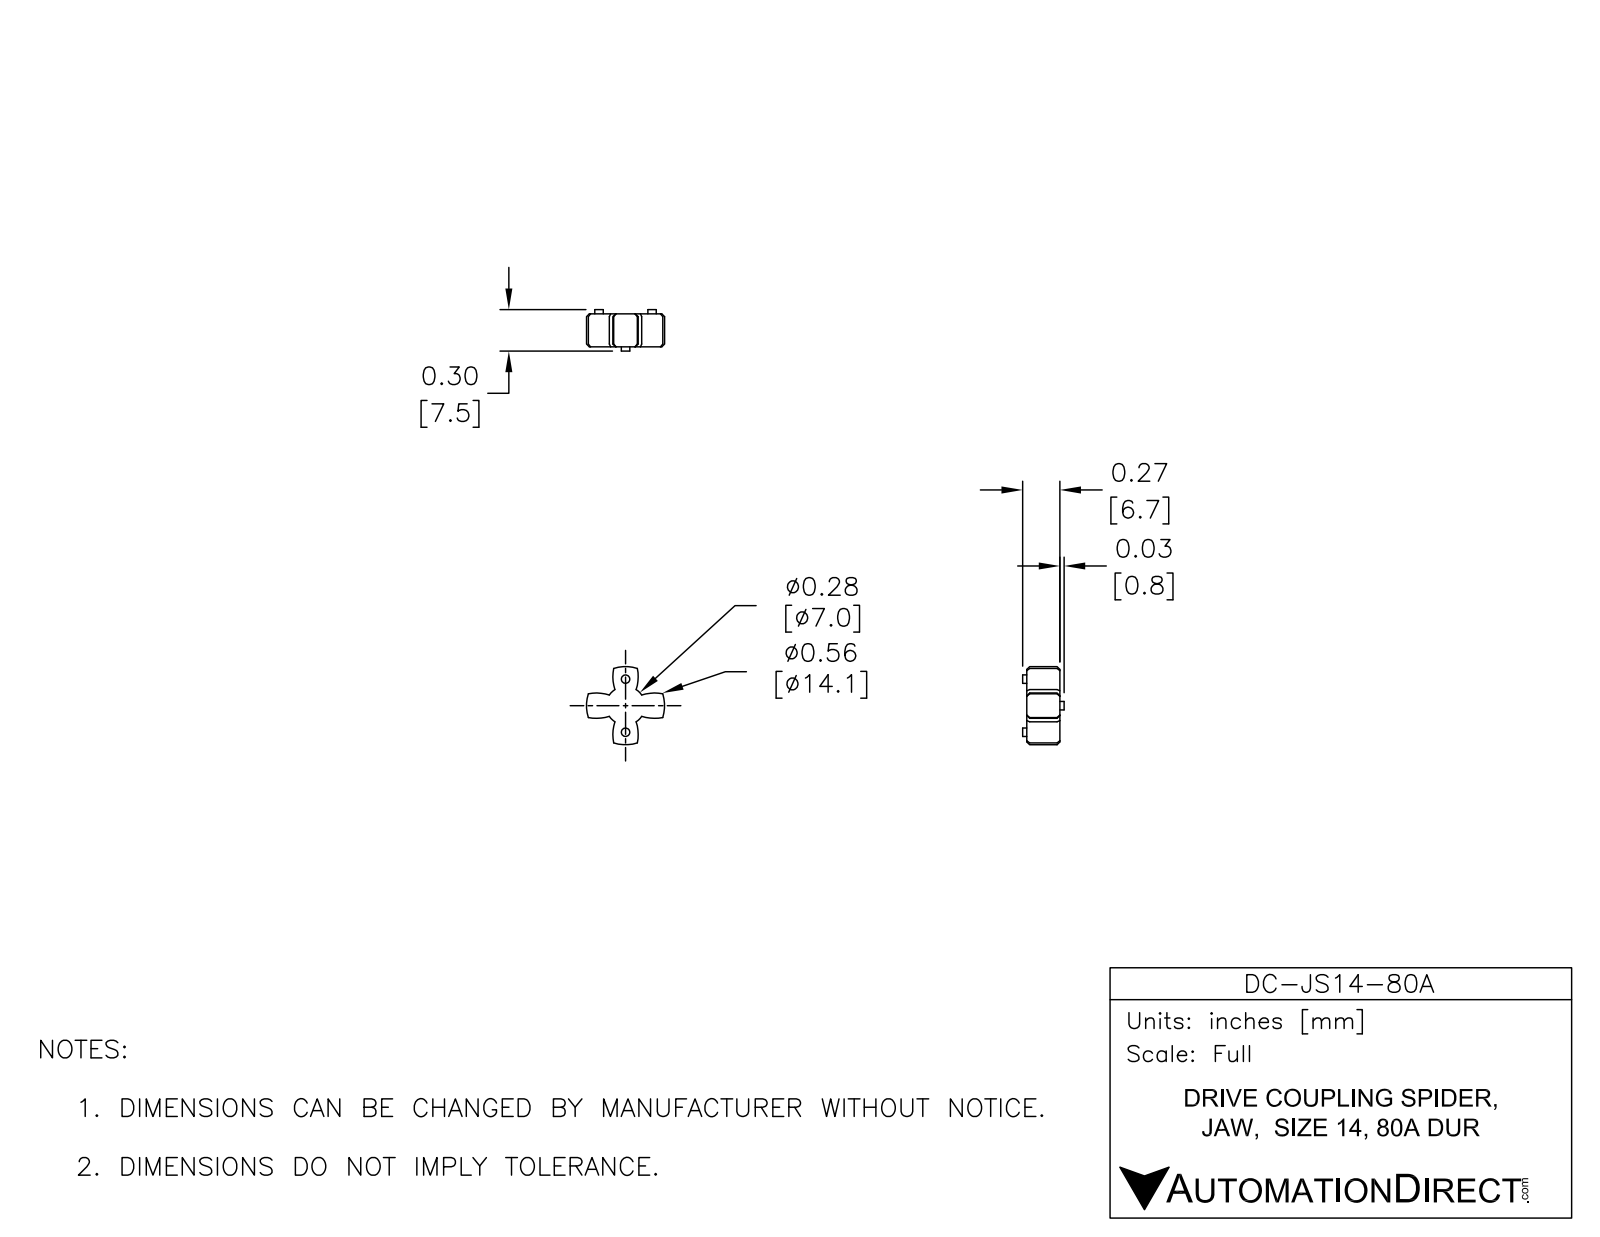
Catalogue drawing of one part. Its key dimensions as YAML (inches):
part_name: "DC-JS14-80A"
step_written_by: "SolidWorks 2015 (AUTOMOTIVE_DESIGN)"
units: inches
bodies: {solids: 1, faces: 71, planar: 6, cylindrical: 27, other: 38}
overall_size: [0.555, 0.555, 0.295]
volume: 0.037
surface_area: 0.789
round_bosses_or_shafts:
  - {diameter: 0.06, count: 4}
partial_cylinders:
  - {radius: 0.296, count: 4}
  - {radius: 0.137, count: 1}
  - {radius: 0.278, count: 1}
face_to_face_distances: [0.235, 0.03, 0.265, 0.295]
